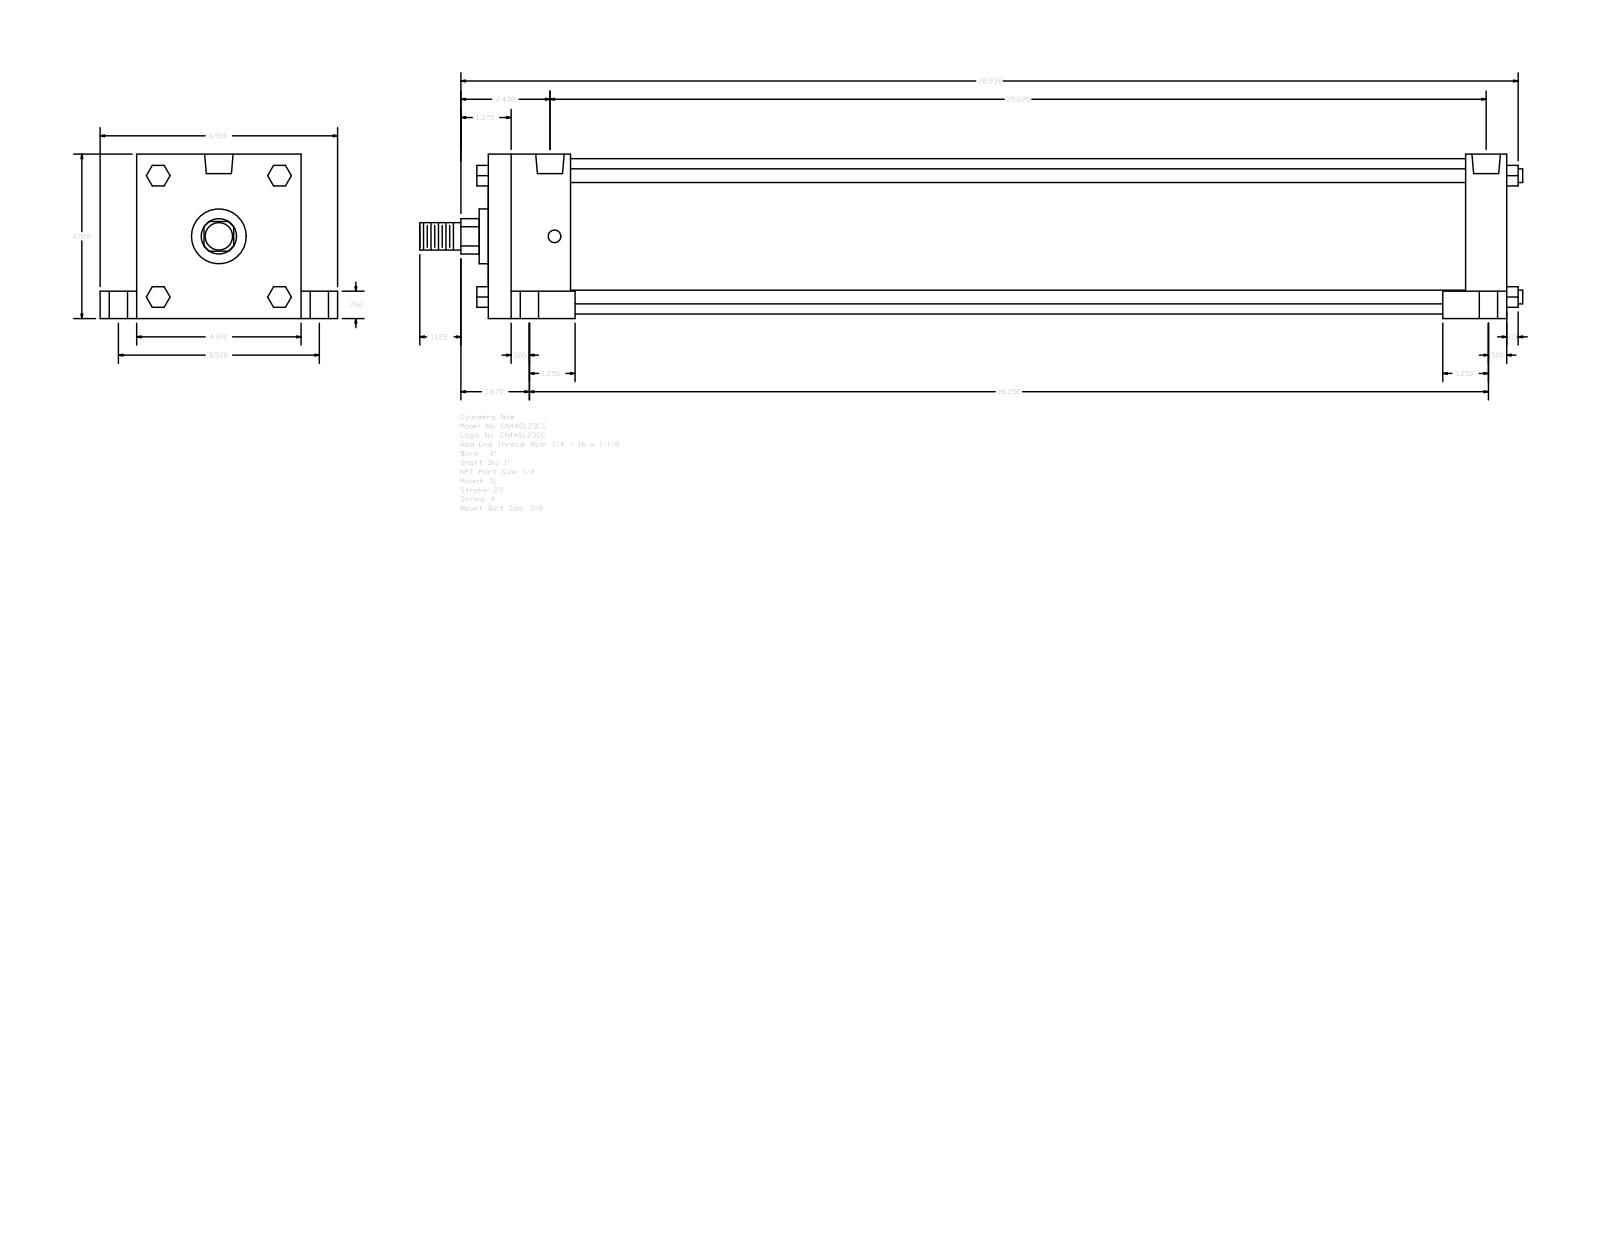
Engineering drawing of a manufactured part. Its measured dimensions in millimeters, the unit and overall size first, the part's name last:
Units: millimetres
Overall size (bounding box): 766.76 × 165.1 × 114.3
Round holes (diameter × count): ⌀8.73 ×4, ⌀12.7 ×4, ⌀19.05 ×4, ⌀19.77 ×2
Round bosses / shafts (diameter × count): ⌀9.53 ×4, ⌀107.95 ×1, ⌀38.1 ×1, ⌀25.4 ×1, ⌀19.05 ×1
Partial cylindrical surfaces — rounded edges, fillets, slot ends (radius × count): R12.29 ×1
Main face-to-face distances: 114.3, 708.03, 57.15, 650.88, 679.45, 622.3, 28.58, 19.05, 25.4, 139.7
Hole centre spacings: 3.18, 69.87, 70.01, 71.3, 72, 139.7, 644.52, 647.7
Bodies: 0 solids, 150 faces (114 planar, 36 cylindrical, 0 other)
Part name (STEP PRODUCT): A_SL__0400_1
STEP written by: GSSL Pune (CONFIG_CONTROL_DESIGN)
